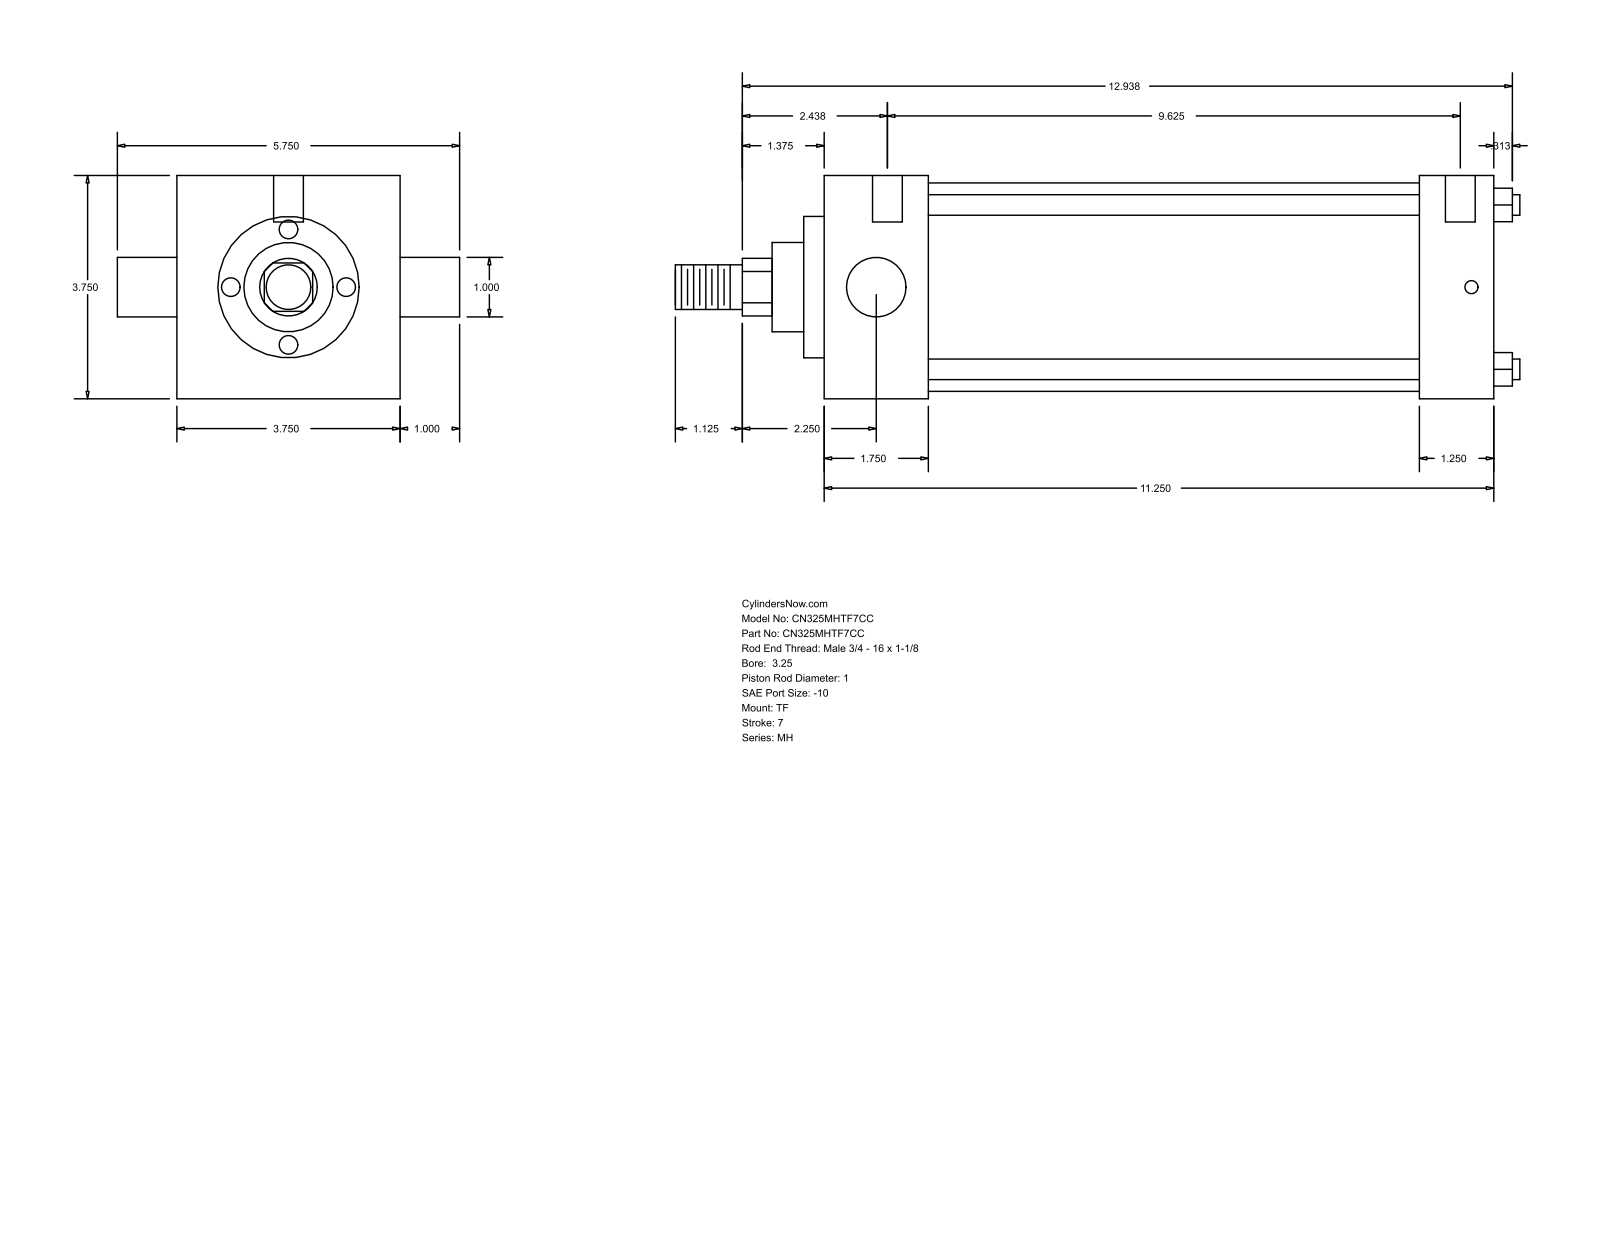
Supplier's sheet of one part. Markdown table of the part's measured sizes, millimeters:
| quantity | value |
| --- | --- |
| part name | MH_TF__0325_1 |
| STEP written by | GSSL Pune (CONFIG_CONTROL_DESIGN) |
| units | millimeters |
| bodies | 0 solids, 86 faces (61 planar, 25 cylindrical, 0 other) |
| overall size | 360.36 × 146.05 × 95.25 |
| round holes (diameter × count) | 5.56 × 3, 12.7 × 2 |
| round bosses / shafts (diameter × count) | 8.76 × 4, 25.4 × 2, 88.9 × 1, 60.33 × 1, 38.1 × 1, 19.05 × 1 |
| partial cylindrical surfaces (radius × count) | 12.29 × 1 |
| main face-to-face distances | 95.24, 285.76, 44.46, 254.01, 209.55, 241.3, 31.75, 8.73, 53.19, 262.74 |
| hole center spacings | 1.58, 4.76, 244.48, 246.06, 249.24, 250.82 |
